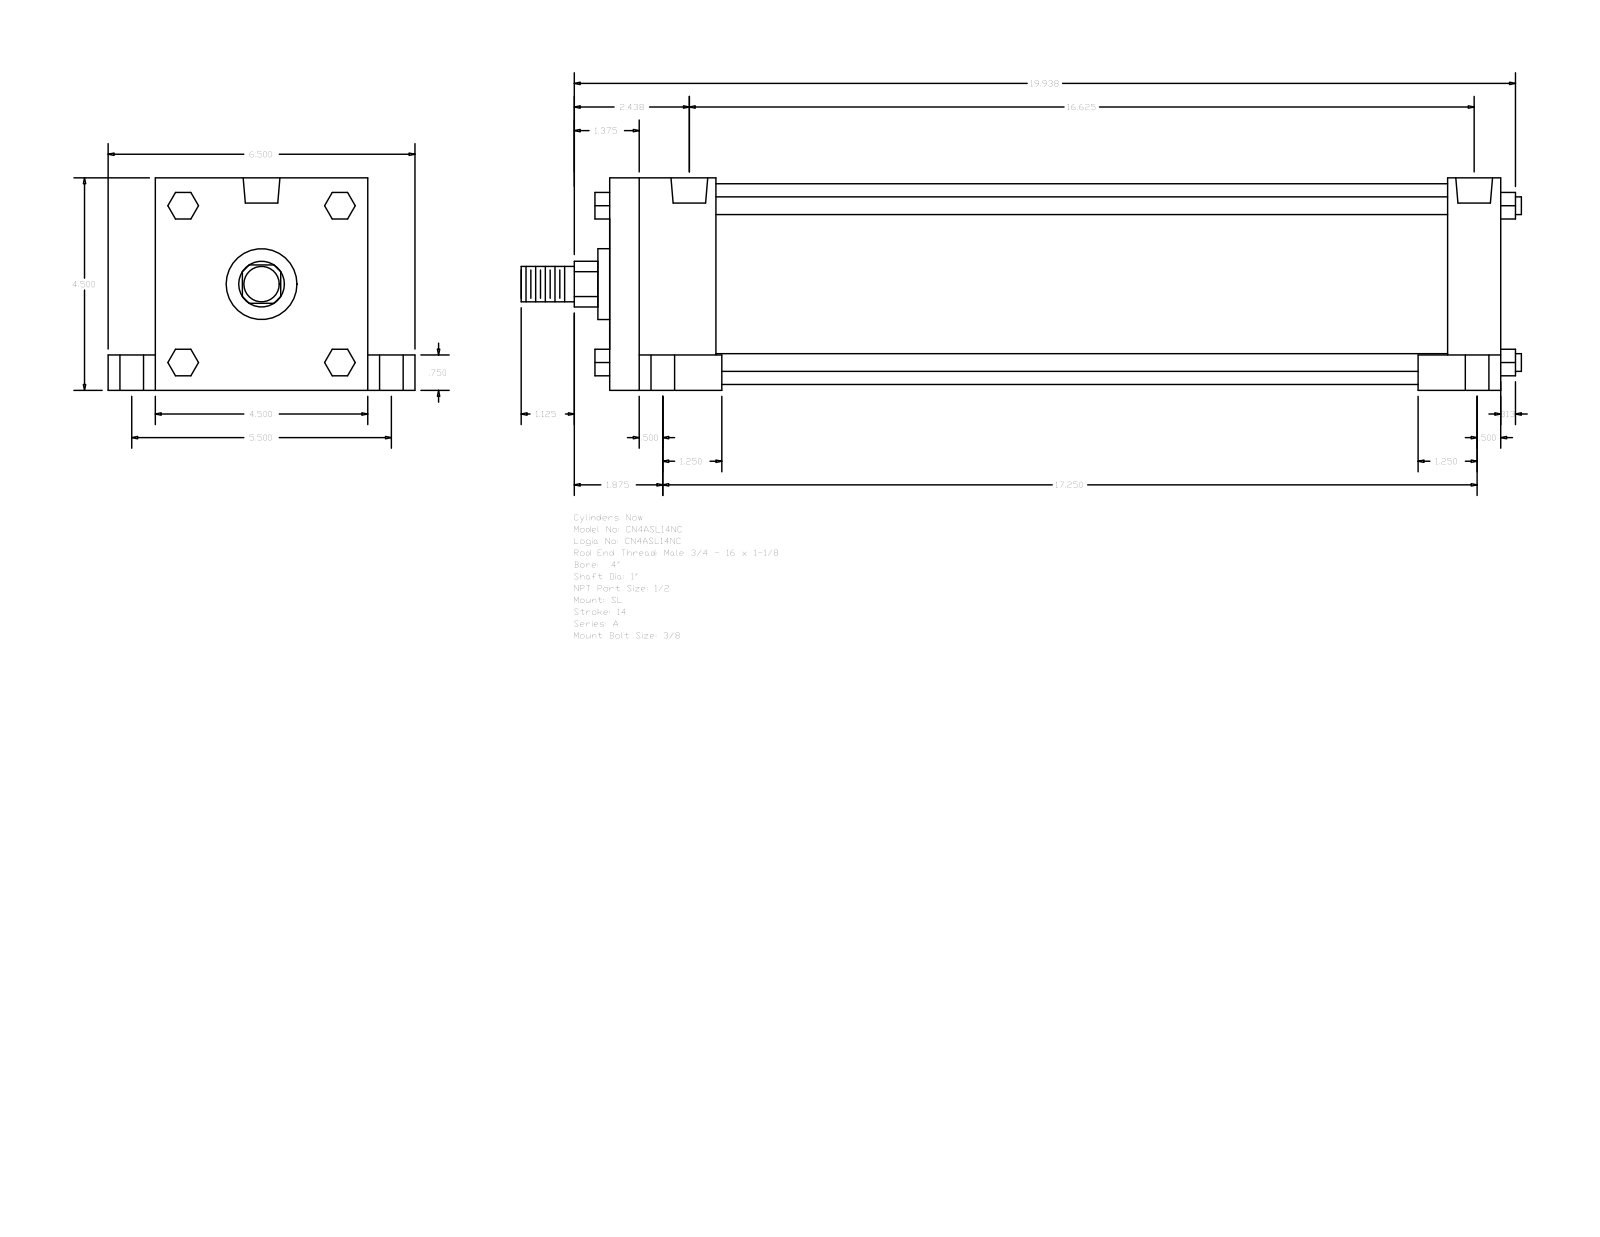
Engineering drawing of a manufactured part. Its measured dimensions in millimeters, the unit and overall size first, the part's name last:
Units: millimetres
Overall size (bounding box): 538.16 × 165.1 × 114.3
Round holes (diameter × count): ⌀8.73 ×4, ⌀12.7 ×4, ⌀19.05 ×4, ⌀19.77 ×2
Round bosses / shafts (diameter × count): ⌀9.53 ×4, ⌀107.95 ×1, ⌀38.1 ×1, ⌀25.4 ×1, ⌀19.05 ×1
Partial cylindrical surfaces — rounded edges, fillets, slot ends (radius × count): R12.29 ×1
Main face-to-face distances: 114.3, 479.43, 57.15, 422.28, 450.85, 393.7, 28.58, 19.05, 25.4, 139.7
Hole centre spacings: 3.18, 69.87, 70.01, 71.3, 72, 139.7, 415.92, 419.1
Bodies: 0 solids, 150 faces (114 planar, 36 cylindrical, 0 other)
Part name (STEP PRODUCT): A_SL__0400_1
STEP written by: GSSL Pune (CONFIG_CONTROL_DESIGN)
